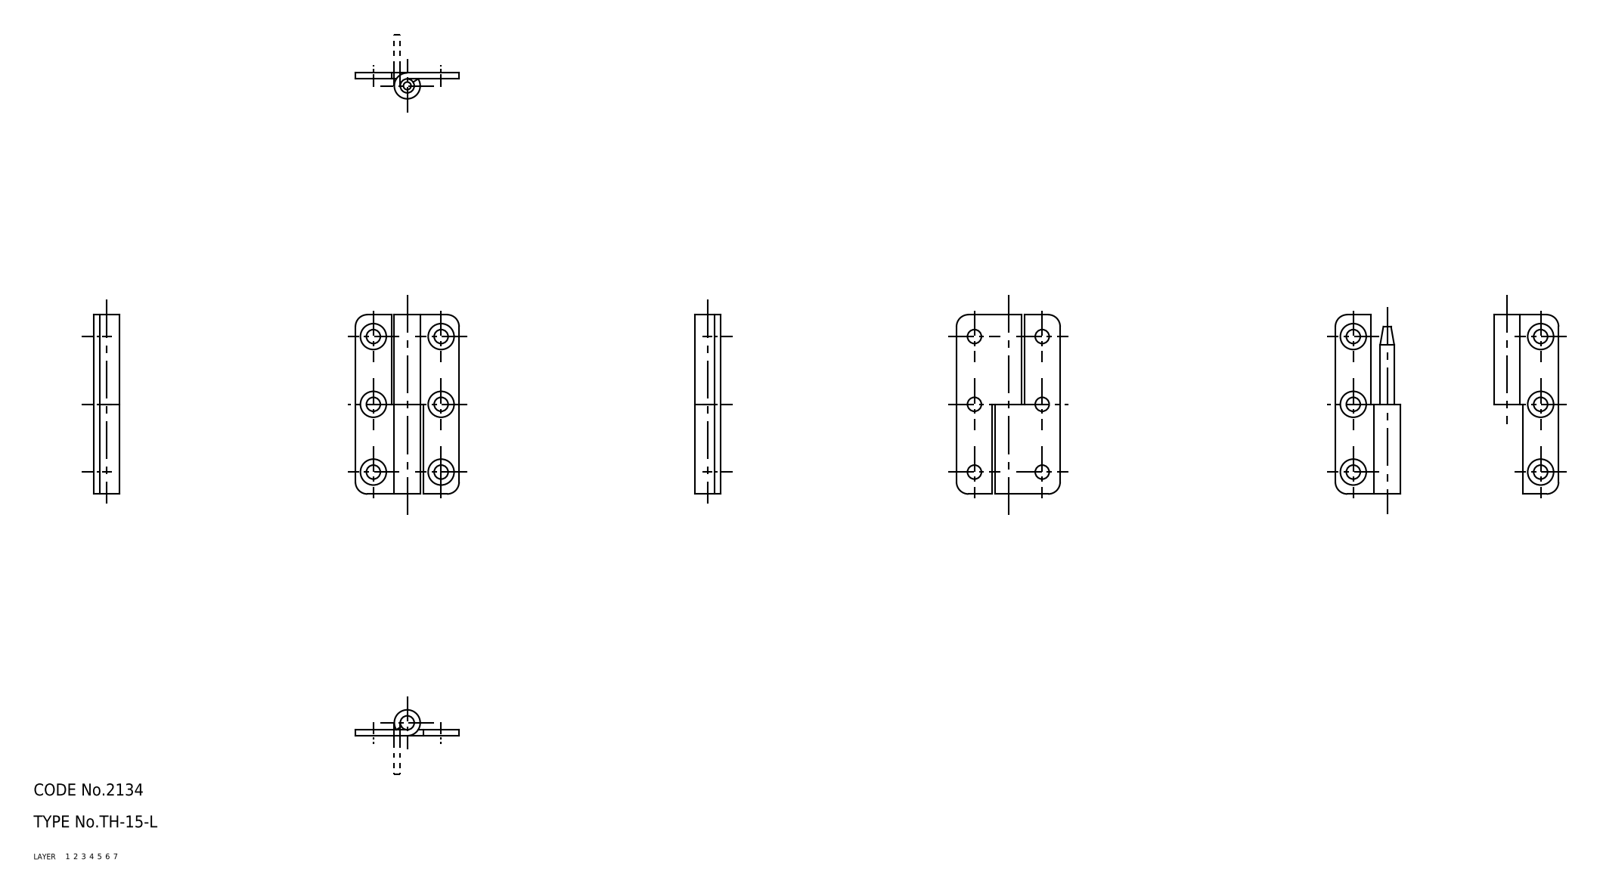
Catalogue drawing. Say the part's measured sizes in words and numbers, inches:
The part is named "67111690; 67111703; 67111716". Its 3-D file was written by "CADfix (AUTOMOTIVE_DESIGN)". It is 3 solids with 42 faces: 0 planar, 0 cylindrical and 42 other. Overall it measures 1.772 by 1.024 by 0.256 inches. Its volume is 0.156 cubic inches and its surface area 6.155 square inches.
